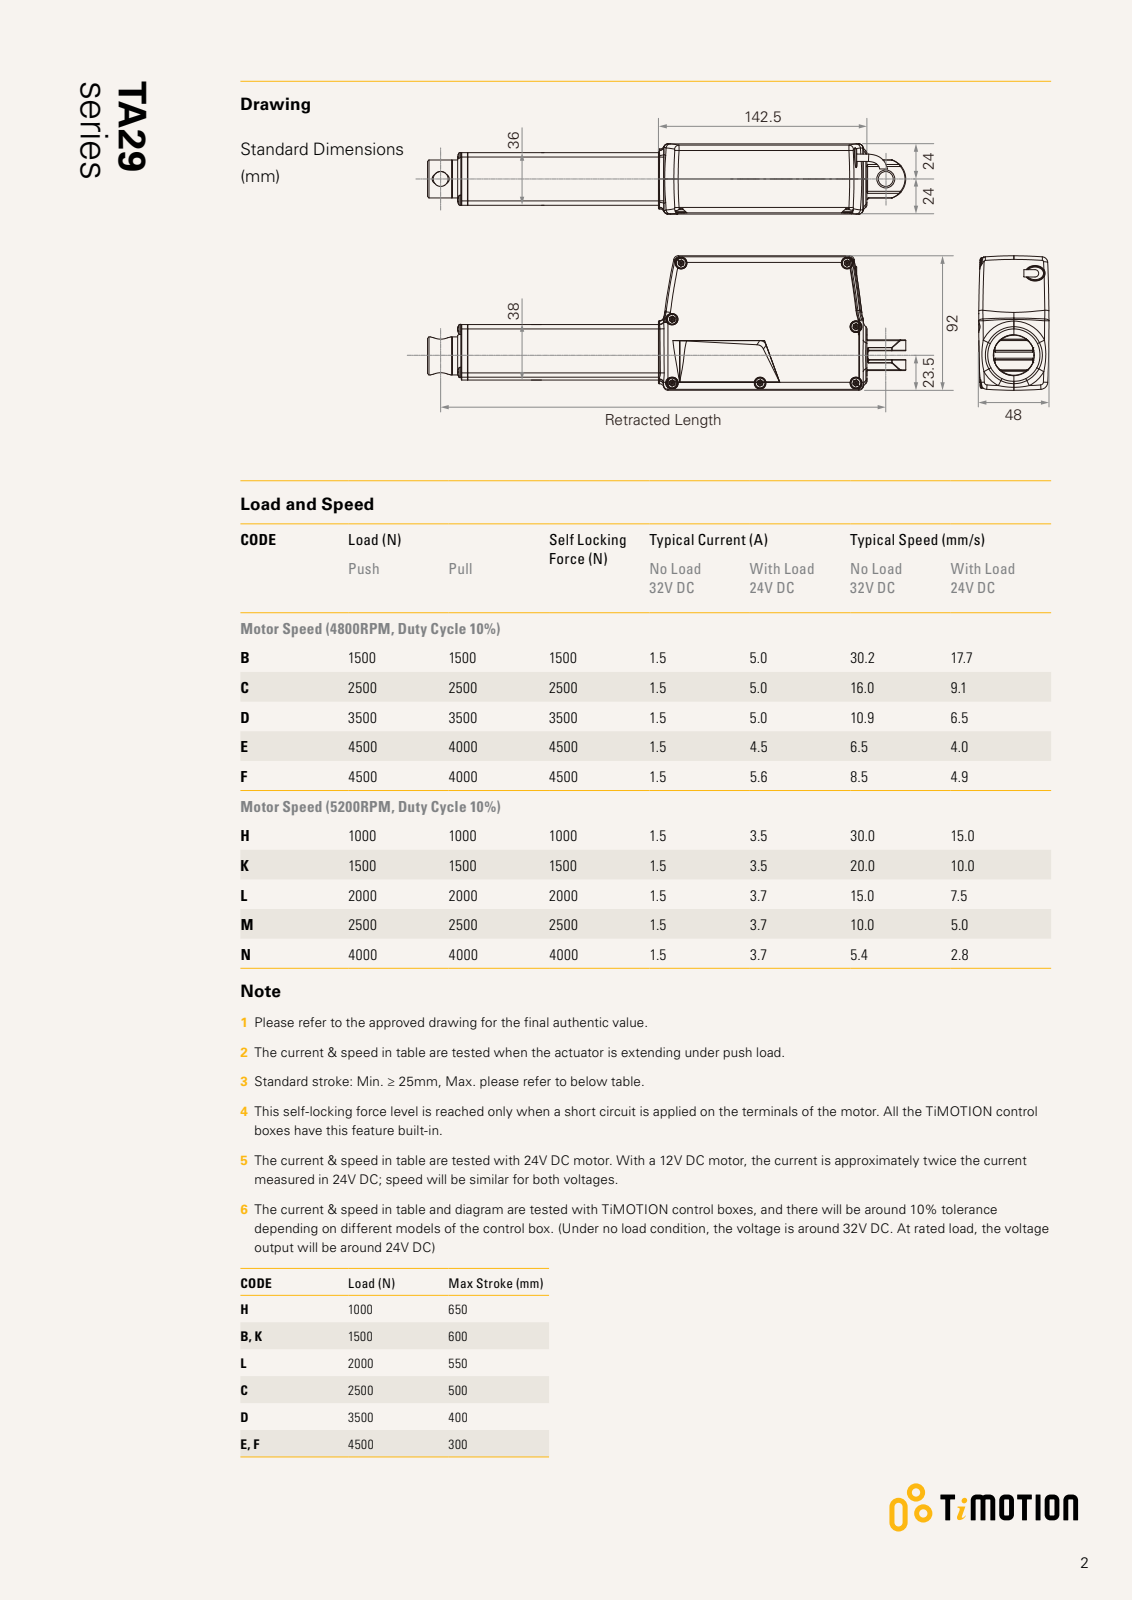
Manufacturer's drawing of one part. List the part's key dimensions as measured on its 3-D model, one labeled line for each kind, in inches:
Part name (STEP PRODUCT): TA29外管 -POT; 內管; M4自攻螺絲 - 複製; M4自攻螺絲 (+7 more)
STEP written by: SolidWorks 2015 (CONFIG_CONTROL_DESIGN)
Units: inches
Bodies: 19 solids, 5098 faces (2191 planar, 1909 cylindrical, 998 other)
Overall size (bounding box): 8.181 × 7.18 × 6.158
Volume: 16.12 in³ · Surface area: 389.8 in²
Round holes (diameter × count): ⌀0.039 ×35, ⌀0.13 ×10, ⌀0.161 ×7, ⌀0.299 ×7, ⌀0.157 ×3, ⌀0.394 ×3, ⌀0.087 ×2, ⌀0.177 ×2, ⌀1.102 ×2, ⌀0.094 ×1, ⌀0.669 ×1, ⌀0.709 ×1
Round bosses / shafts (diameter × count): ⌀0.157 ×11, ⌀0.287 ×8, ⌀0.093 ×8, ⌀0.276 ×3, ⌀0.079 ×2, ⌀1.102 ×1, ⌀1.024 ×1, ⌀0.866 ×1
Partial cylindrical surfaces — rounded edges, fillets, slot ends (radius × count): R0.02 ×170, R0.012 ×122, R0.024 ×37, R0.008 ×34, R0.079 ×23, R0.031 ×20, R0.039 ×16, R0.059 ×11
Main face-to-face distances: 0.059, 1.359, 1.418, 1.3, 0.047, 0.062, 0.12, 1.426, 1.423, 1.364
Hole centre spacings: 0.675, 21.386, 0.646, 0.612, 0.739, 0.394, 0.737, 1.157
